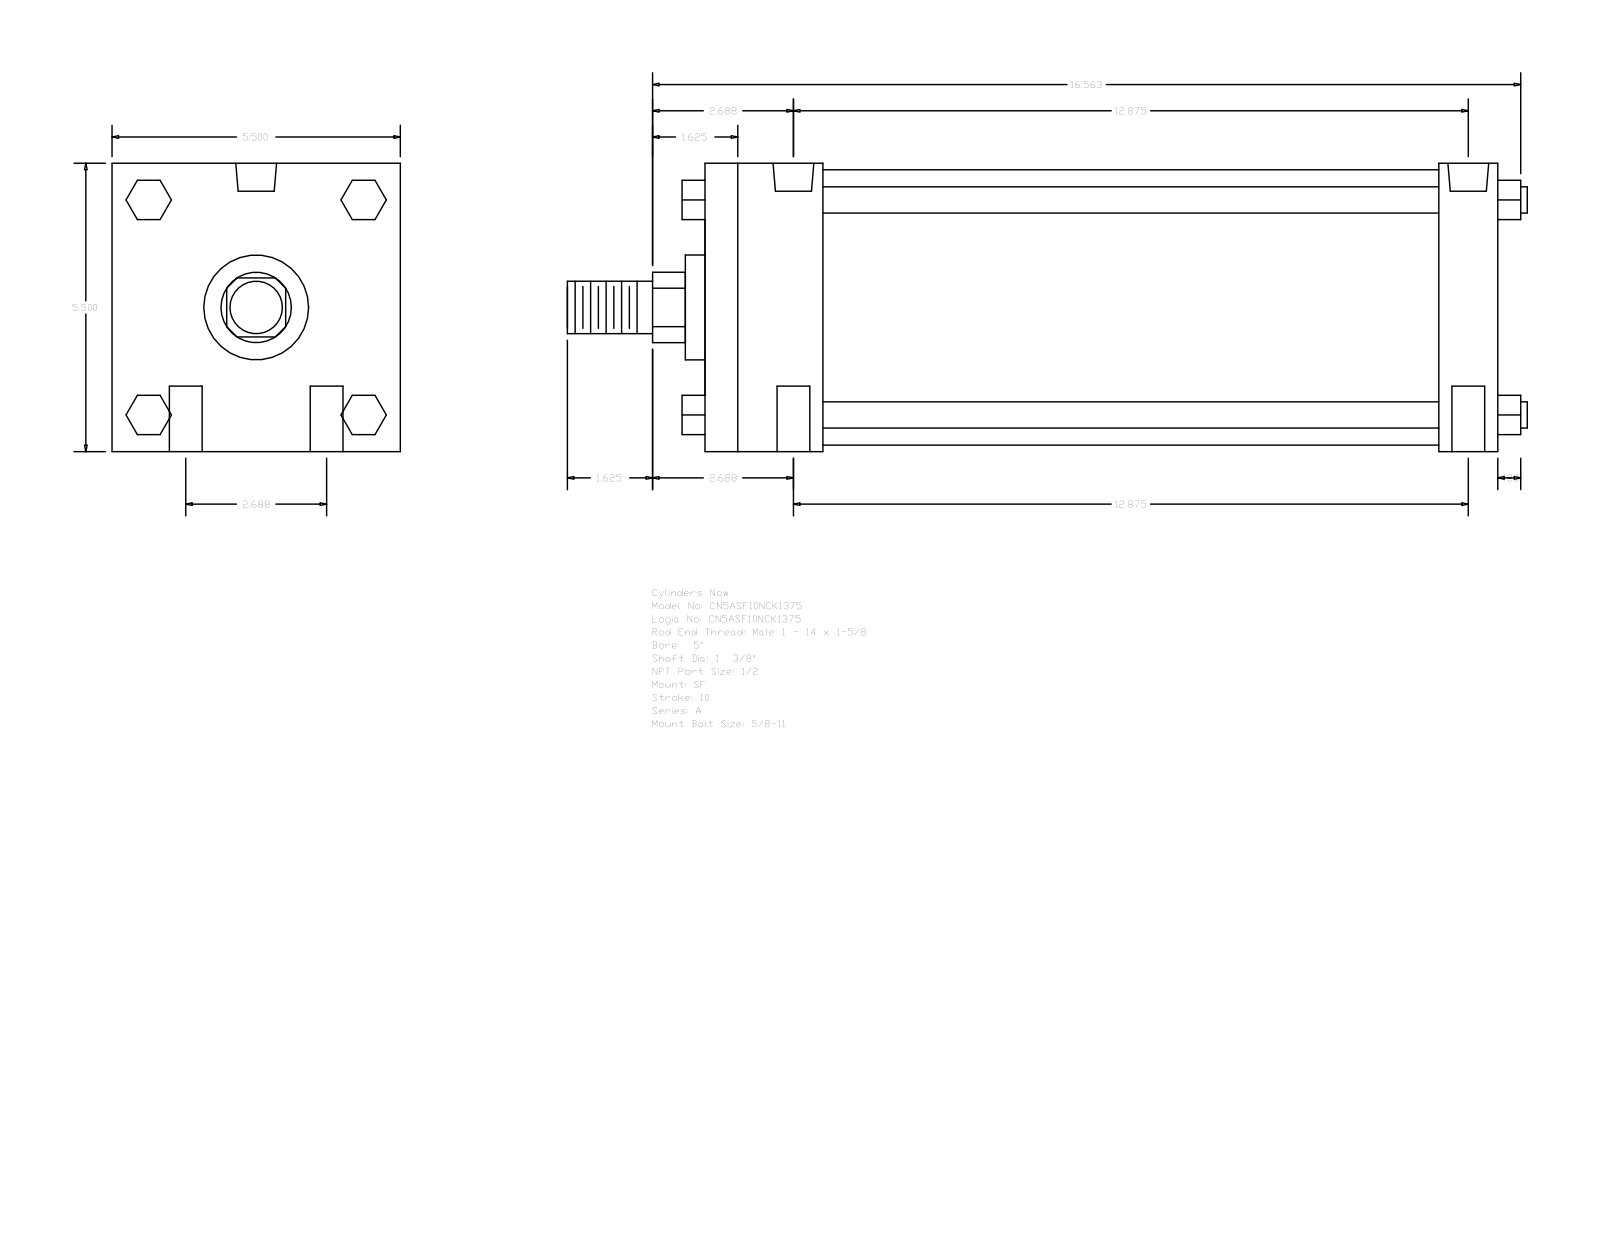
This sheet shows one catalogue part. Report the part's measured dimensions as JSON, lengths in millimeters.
{"part_name": "A_SF__0500_1.375", "step_written_by": "GSSL Pune (CONFIG_CONTROL_DESIGN)", "units": "millimeters", "bodies": {"solids": 0, "faces": 124, "planar": 94, "cylindrical": 30, "other": 0}, "overall_size": [465.14, 139.7, 139.7], "round_holes": [[15.88, 4], [8.73, 2], [19.77, 2]], "round_bosses_or_shafts": [[12.7, 4], [133.35, 1], [50.8, 1], [34.92, 1], [25.4, 1]], "partial_cylinders_radius": [[17.06, 1]], "face_to_face_distances": [139.7, 384.17, 57.15, 355.6, 298.45, 327.02, 28.57, 19.05, 52.07, 90.18], "hole_center_spacings": [34.13, 328.81, 327.03, 68.26, 334.08, 322.25]}
